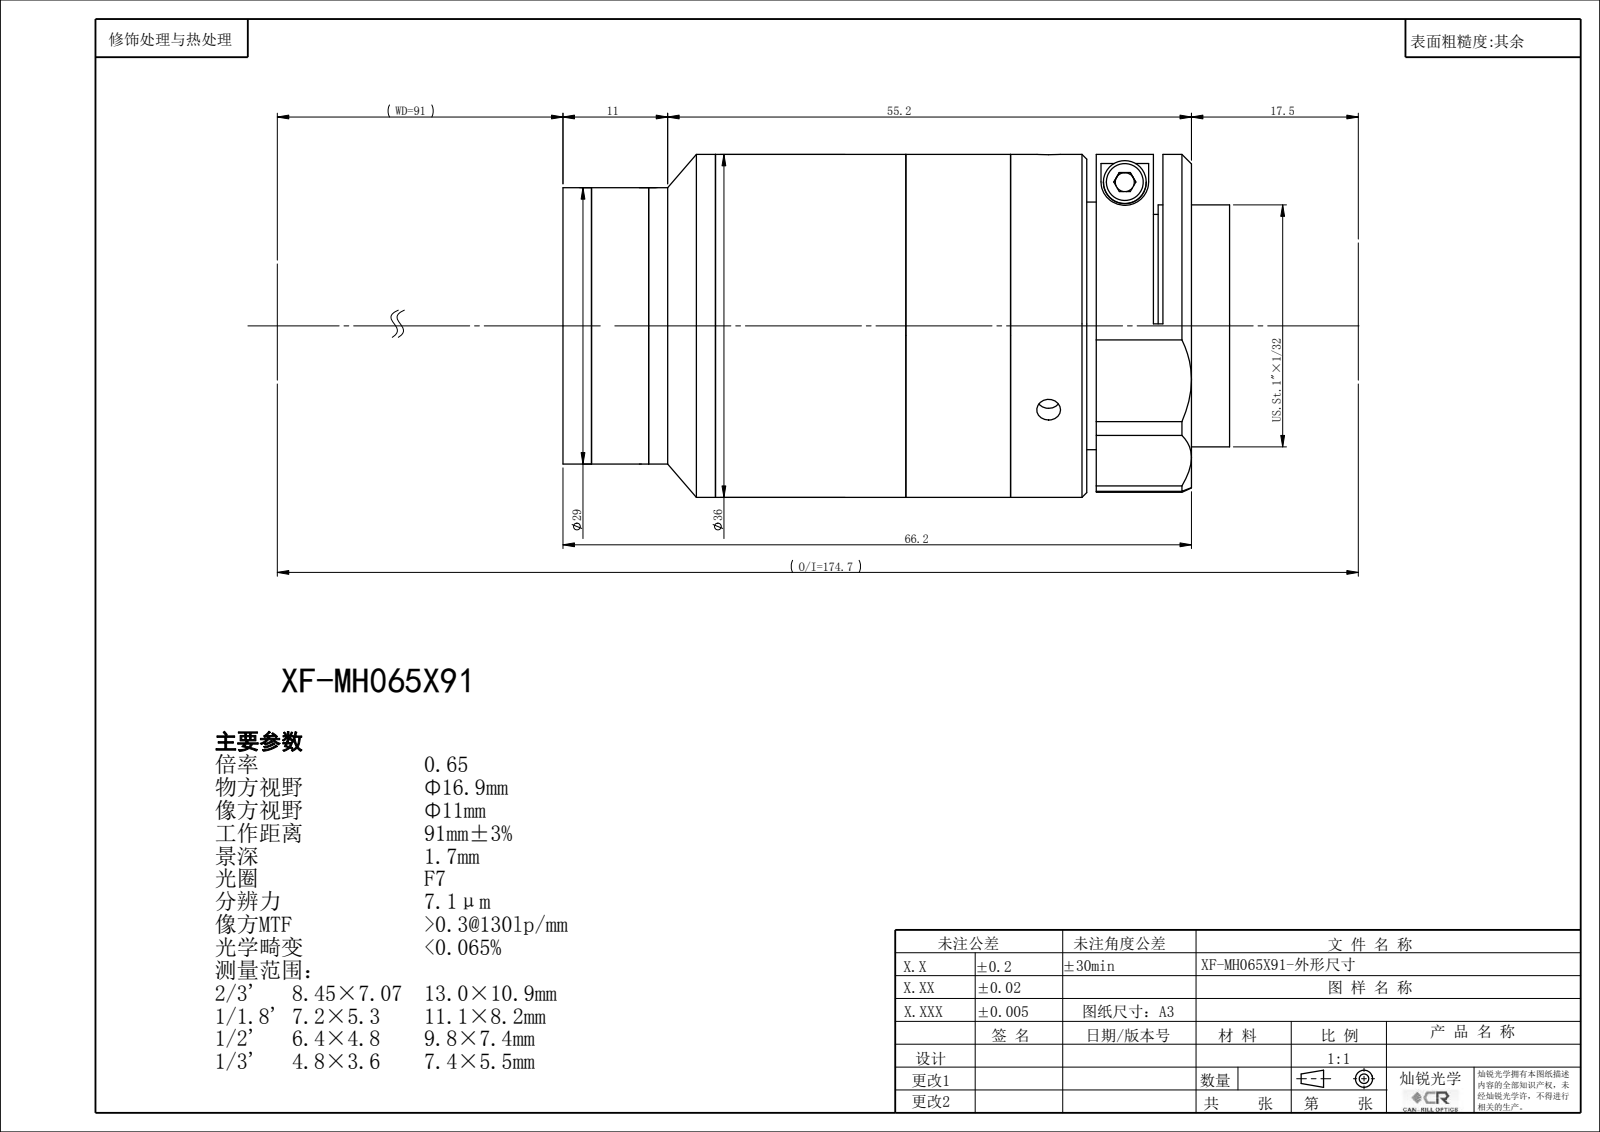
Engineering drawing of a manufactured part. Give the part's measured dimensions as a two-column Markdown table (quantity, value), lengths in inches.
| quantity | value |
| --- | --- |
| part name | XF-MH065X91 |
| STEP written by | SolidWorks 2022 (CONFIG_CONTROL_DESIGN) |
| units | inches |
| bodies | 0 solids, 130 faces (66 planar, 42 cylindrical, 22 other) |
| overall size | 2.767 × 1.418 × 1.417 |
| round holes (diameter × count) | 0.098 × 3, 0.551 × 1, 0.882 × 1, 0.945 × 1, 0.98 × 1, 1.039 × 1, 1.063 × 1 |
| round bosses / shafts (diameter × count) | 1.417 × 1, 1.339 × 1, 1.142 × 1, 1 × 1 |
| main face-to-face distances | 0.758, 0.787, 1.702, 2.46, 0.059, 2.401, 0.699, 1.269, 0.433, 1.132 |
